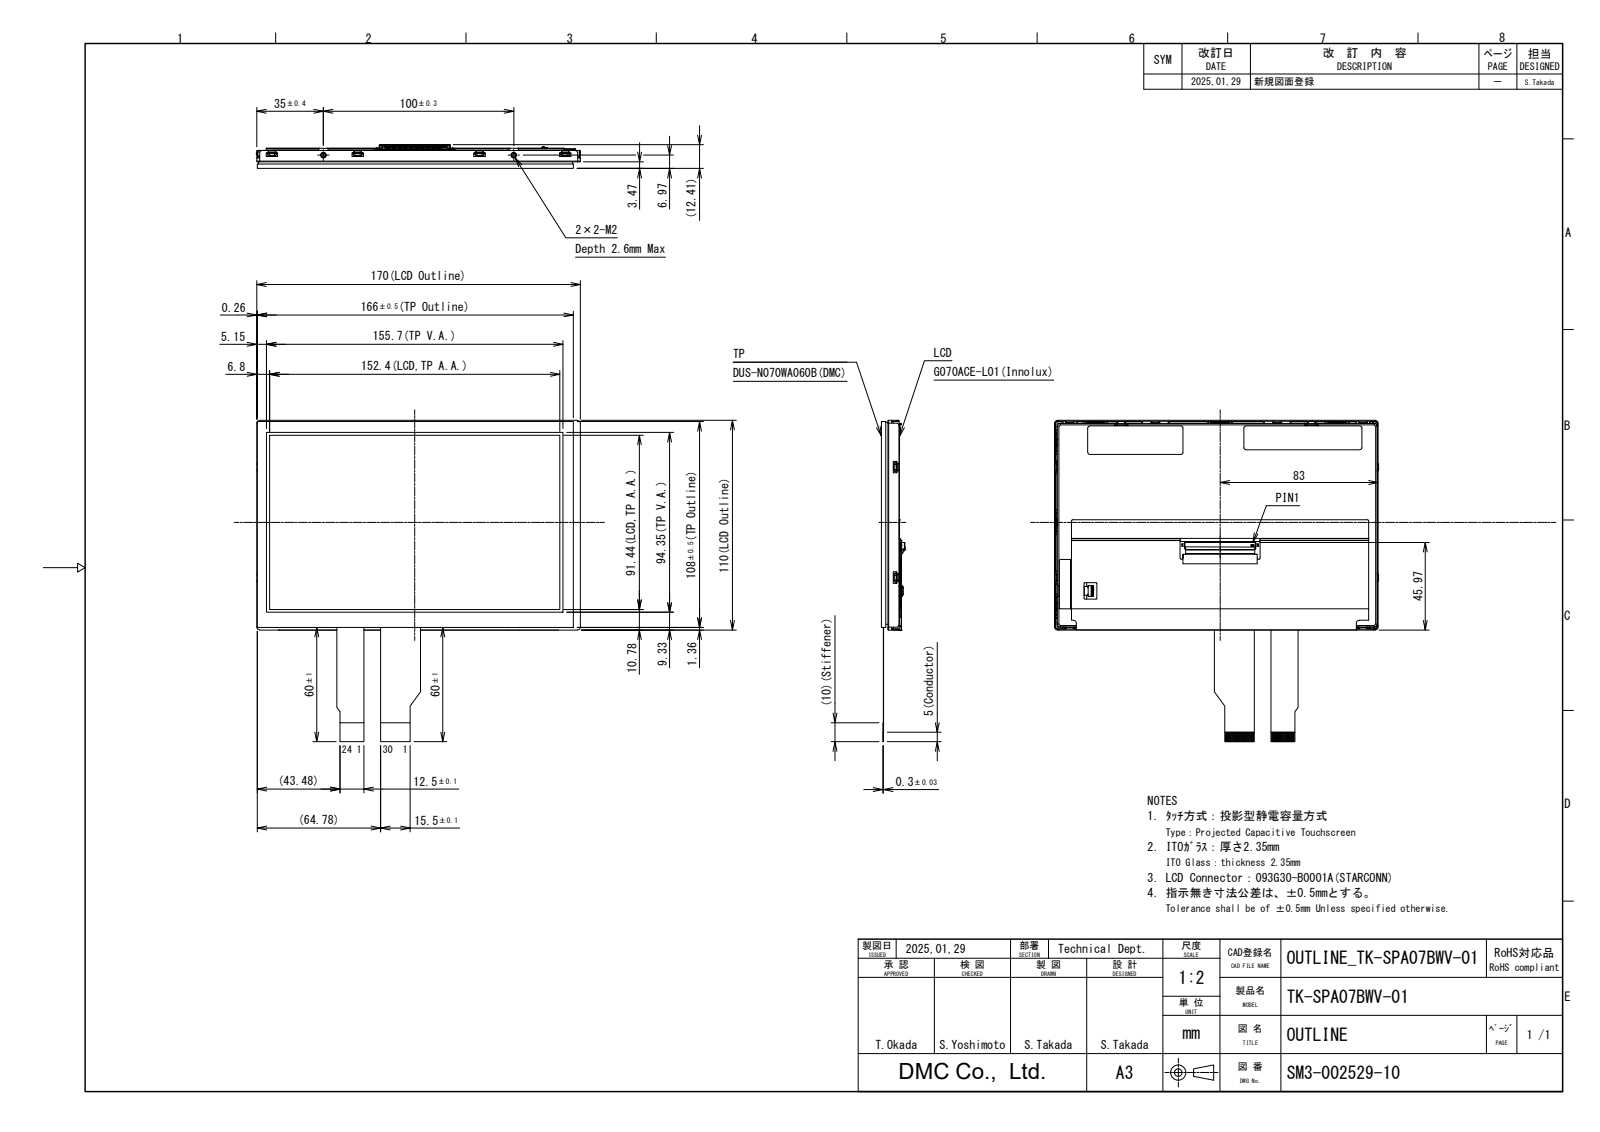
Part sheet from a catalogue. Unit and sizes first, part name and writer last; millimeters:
Units: millimetres
Overall size (bounding box): 170.2 × 168.65 × 12.41
Round holes (diameter × count): ⌀0.4 ×4, ⌀2.4 ×4, ⌀2 ×2, ⌀3 ×2, ⌀5 ×2, ⌀8.4 ×1, ⌀9 ×1
Round bosses / shafts (diameter × count): ⌀2 ×4, ⌀3.4 ×2, ⌀10.6 ×1, ⌀10 ×1
Partial cylindrical surfaces — rounded edges, fillets, slot ends (radius × count): R0.5 ×251, R0.2 ×115, R0.3 ×77, R1 ×54, R0.1 ×25, R1.1 ×23, R0.6 ×21, R0.85 ×14
Main face-to-face distances: 6.32, 1.75, 0.8, 9.47, 2.35, 8.67, 7.12, 4.76, 3.96, 2.36
Hole centre spacings: 127.08, 133.5, 11.35, 11.36, 132.43, 133.64, 134.42, 15.86
Volume: 81 341 mm³ · Surface area: 166 670 mm²
Bodies: 1 solid, 5011 faces (3604 planar, 1188 cylindrical, 219 other)
Part name (STEP PRODUCT): HP_TK-SPA07BWV-01
STEP written by: Autodesk Inventor 2020 (AUTOMOTIVE_DESIGN)
